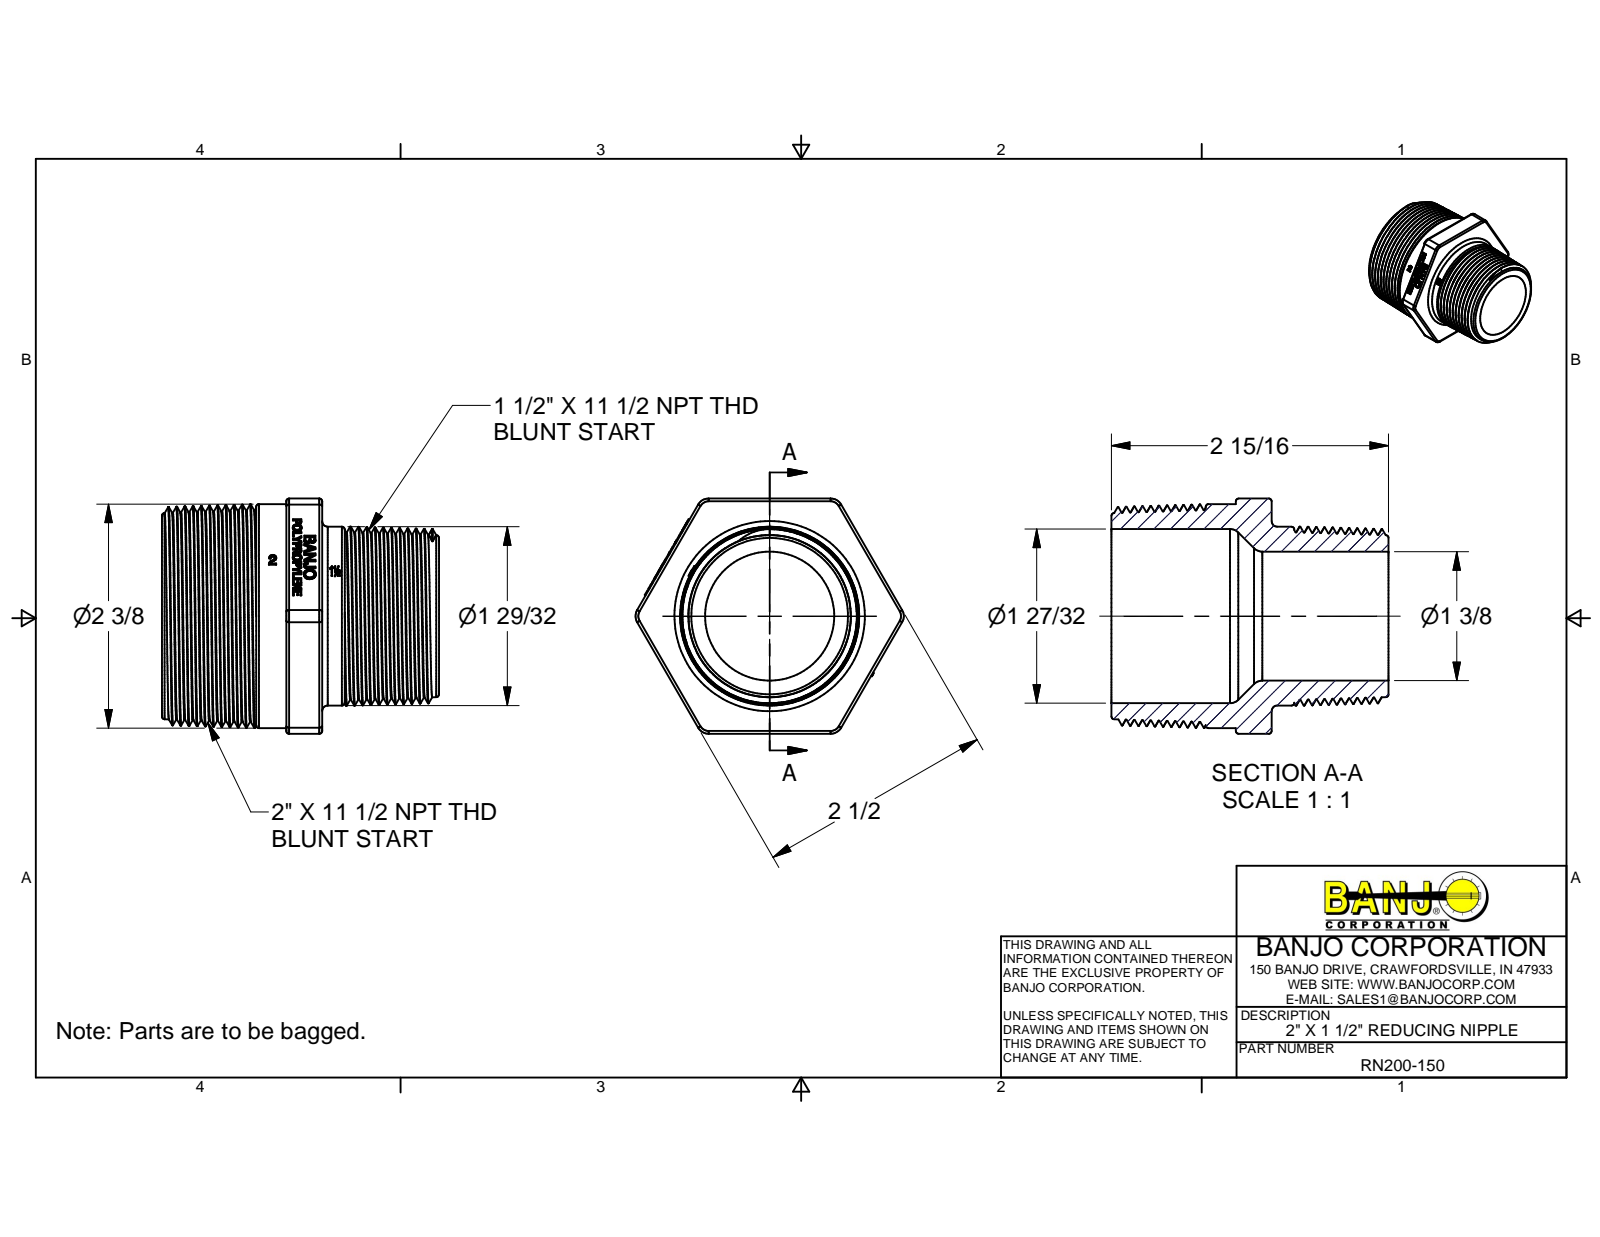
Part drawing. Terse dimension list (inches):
name: RN200-150
written by: Autodesk Inventor 2014 (AUTOMOTIVE_DESIGN)
unit: in
bodies: 1 solid, 410 faces (205 planar, 30 cylindrical, 175 other)
size: 2.94 × 2.846 × 2.5
volume: 4.741 in³; area: 50.6 in²
holes: 1× ⌀1.37, 1× ⌀1.85
bosses: 1× ⌀2.38, 1× ⌀1.9
rounds: 12× R0.03, 6× R0.13, 1× R0.494, 1× R0.611, 1× R0.96, 1× R1.2
face distances: 2.5, 1.7, 1.32, 0.38, 2.94, 1.62, 1.24, 1, 1.94, 0.32
